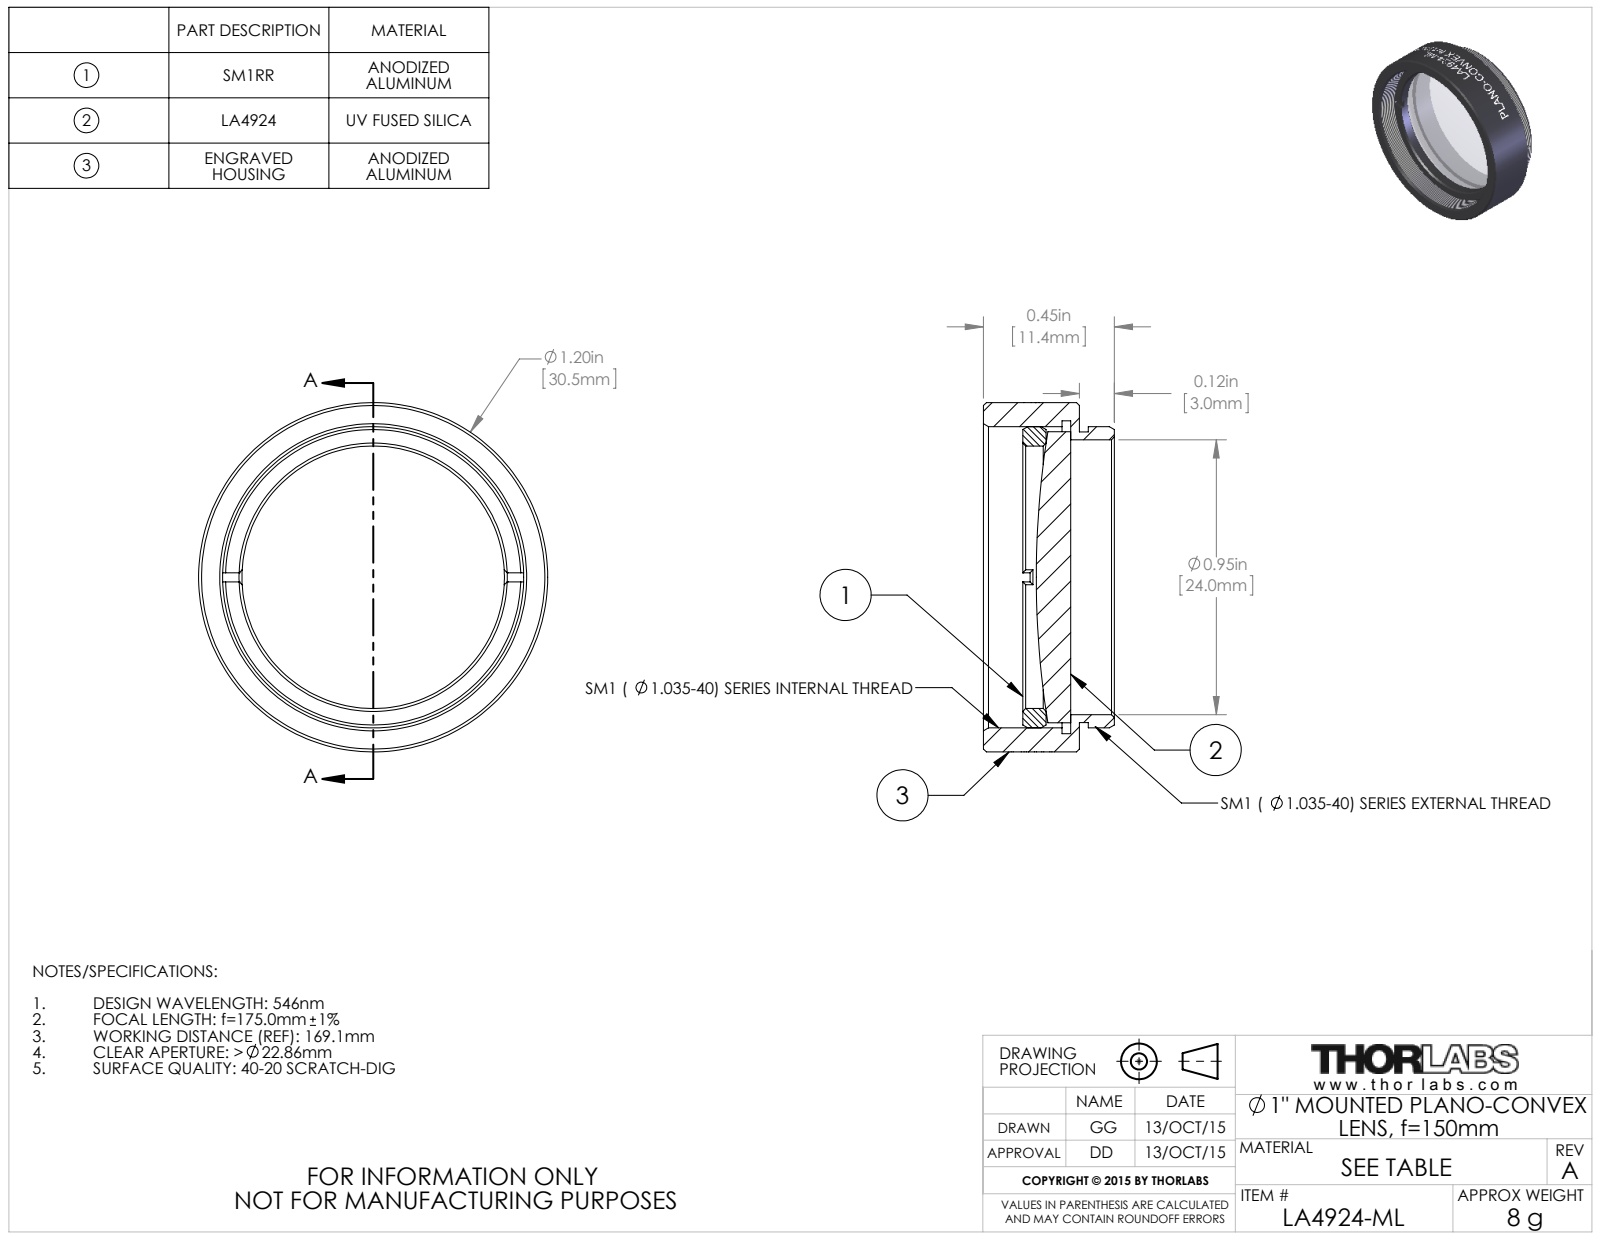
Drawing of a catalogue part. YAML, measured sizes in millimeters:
part_name: "TTN039437-E0W"
step_written_by: "SolidWorks 2014 (CONFIG_CONTROL_DESIGN)"
units: millimeters
bodies: {solids: 3, faces: 123, planar: 20, cylindrical: 79, other: 24}
overall_size: [30.48, 30.48, 11.43]
volume: 3351
surface_area: 4316
round_holes:
  - {diameter: 22.91, count: 1}
  - {diameter: 24, count: 1}
  - {diameter: 27.31, count: 1}
round_bosses_or_shafts:
  - {diameter: 30.48, count: 1}
  - {diameter: 26.29, count: 1}
  - {diameter: 25.4, count: 1}
  - {diameter: 25.37, count: 1}
face_to_face_distances: [0.76, 8.38, 7.62, 2.92, 2.16, 5.46, 4.95, 4.19, 2.03, 3.43]
